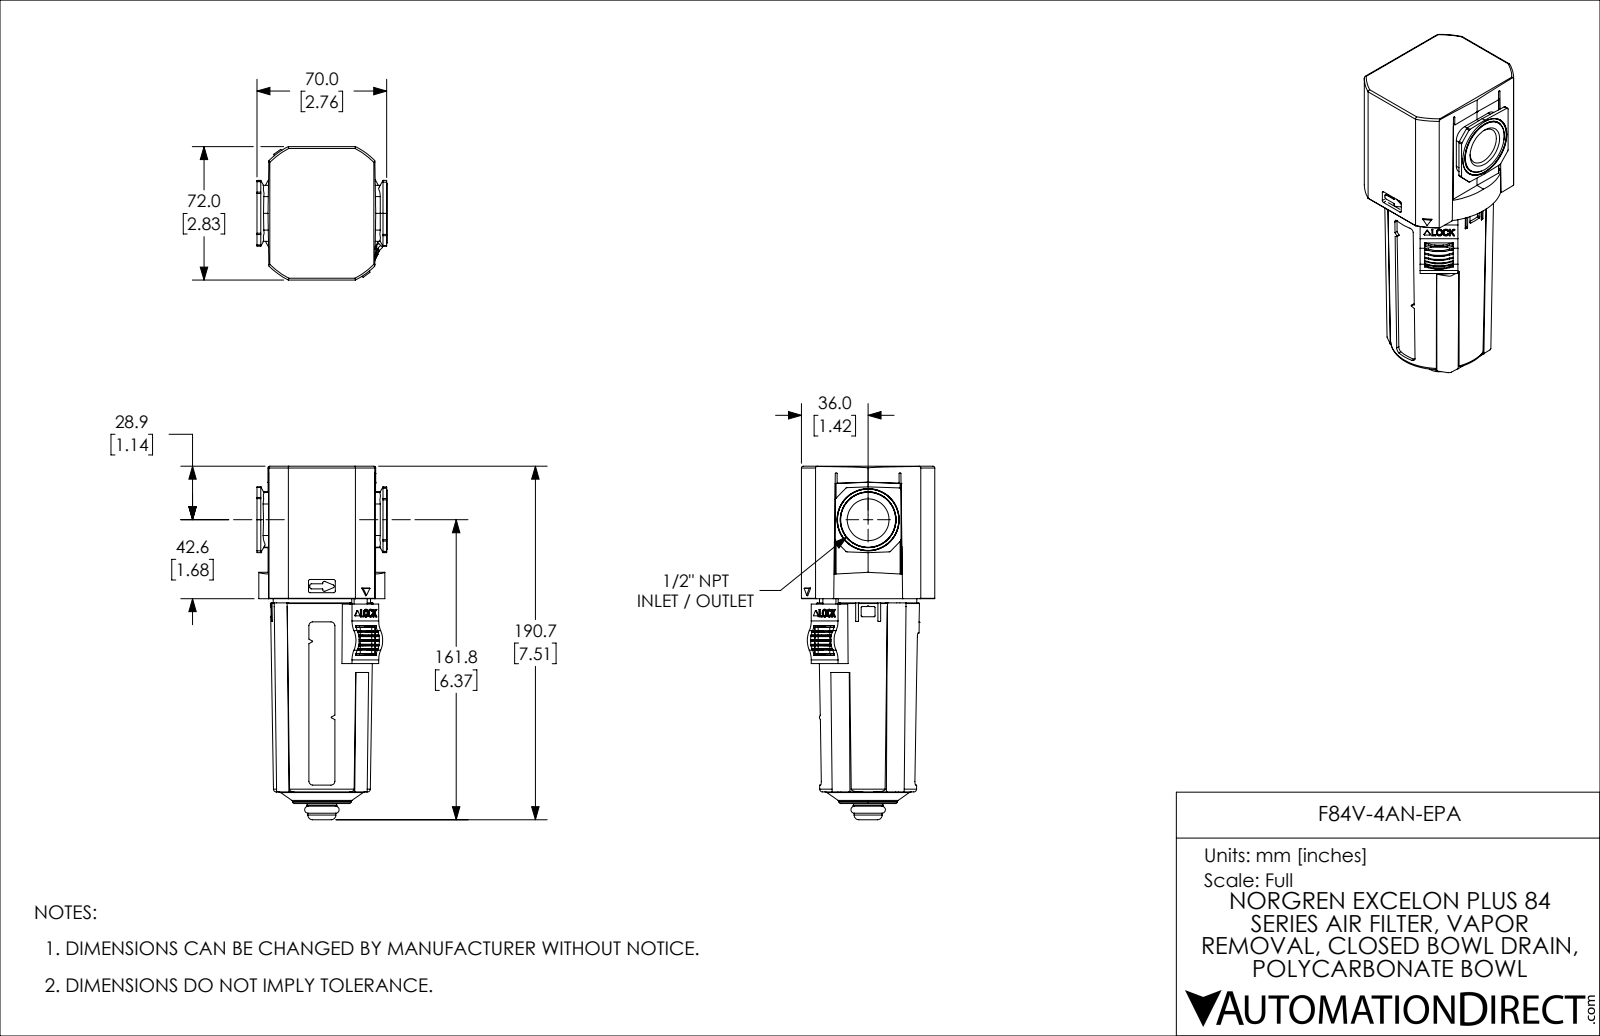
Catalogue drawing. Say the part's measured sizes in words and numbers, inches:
The part is named "F84V-4AN-EPA". Its 3-D file was written by "SolidWorks 2021 (CONFIG_CONTROL_DESIGN)". It is 5 solids with 994 faces: 438 planar, 366 cylindrical and 190 other. Overall it measures 7.508 by 2.835 by 2.766 inches. Its volume is 27.64 cubic inches and its surface area 146.9 square inches. Round holes: 2 of diameter 0.163, 1 of diameter 0.126, 1 of diameter 0.268, 1 of diameter 0.969, 1 of diameter 2.461. Round bosses or shafts: 2 of diameter 0.315, 2 of diameter 0.276, 1 of diameter 0.906, 1 of diameter 0.626, 1 of diameter 0.594, 1 of diameter 0.399. Partial cylindrical surfaces (rounded edges, fillets, slot ends): 40 of radius 0.02, 32 of radius 0.039, 24 of radius 0.01, 16 of radius 0.028, 10 of radius 0.008, 8 of radius 0.038, 8 of radius 0.045, 8 of radius 0.06. The main face-to-face distances are 0.059, 2.352, 2.411, 2.835, 0.035, 2.317, 2.376, 2.756, 0.404, 0.439. The hole center spacings are 0.594, 1.189.
